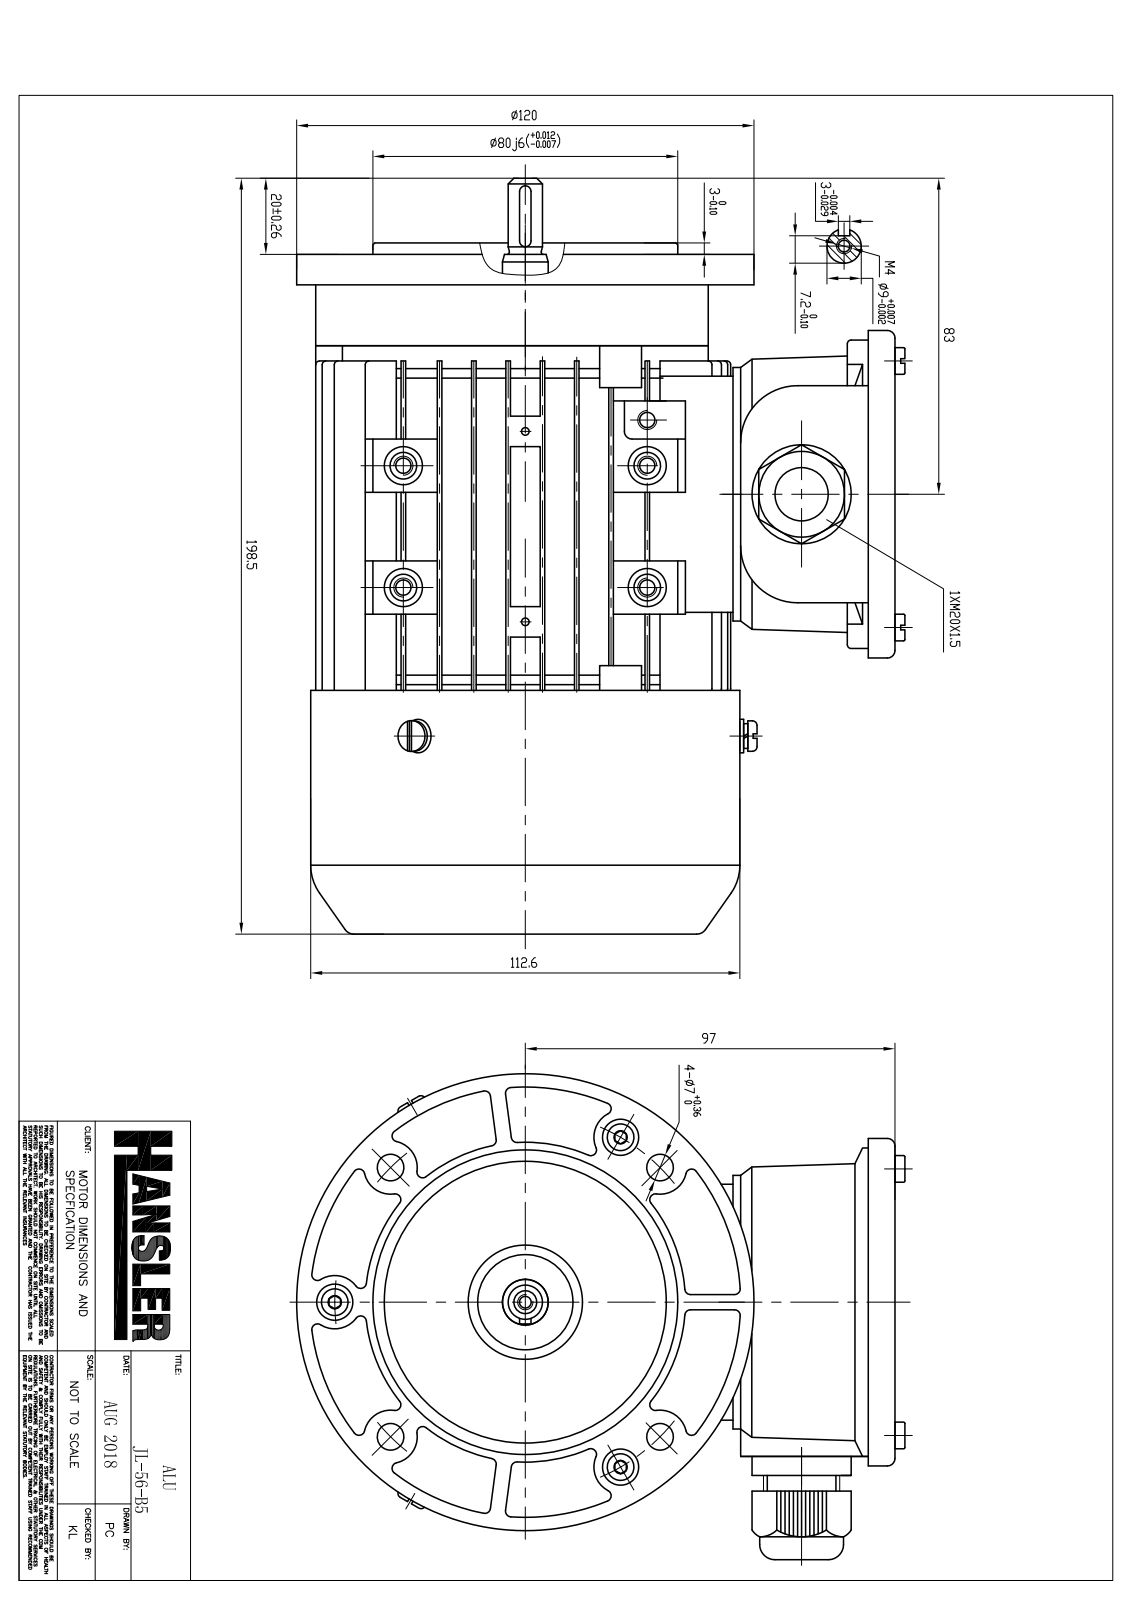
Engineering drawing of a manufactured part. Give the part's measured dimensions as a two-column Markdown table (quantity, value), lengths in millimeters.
| quantity | value |
| --- | --- |
| part name | JL-56-B5 |
| STEP written by | SIEMENS PLM Software NX 12.0 (AP203_CONFIGURATION_CONTROLLED_3D_DESIGN_OF_MECHANICAL_PARTS_AND_ASSEMBLIES_MIM_LF) |
| units | millimeters |
| bodies | 34 solids, 2823 faces (1564 planar, 974 cylindrical, 285 other) |
| overall size | 198.42 × 158.4 × 123.58 |
| volume | 410 751 mm³ |
| surface area | 331 577 mm² |
| round holes (diameter × count) | 3 × 18, 4 × 13, 10 × 8, 4.7 × 7, 4.25 × 6, 5 × 4, 7 × 4, 2 × 3, 4.9 × 3, 9.5 × 3, 12 × 3, 4.13 × 1 |
| round bosses / shafts (diameter × count) | 7 × 11, 3.55 × 10, 4 × 9, 6.45 × 6, 11 × 2, 120 × 1, 112.6 × 1, 96 × 1 |
| partial cylindrical surfaces (radius × count) | 0.5 × 260, 1.5 × 52, 3 × 36, 5 × 16, 2 × 11, 7 × 7, 2.5 × 6, 1 × 5 |
| main face-to-face distances | 8.68, 17.36, 2, 26.04, 1.2, 9.88, 34.72, 7.48, 4, 18.56 |
| hole center spacings | 44, 58.46, 32, 50, 65.3, 12, 17.63, 18.38 |
